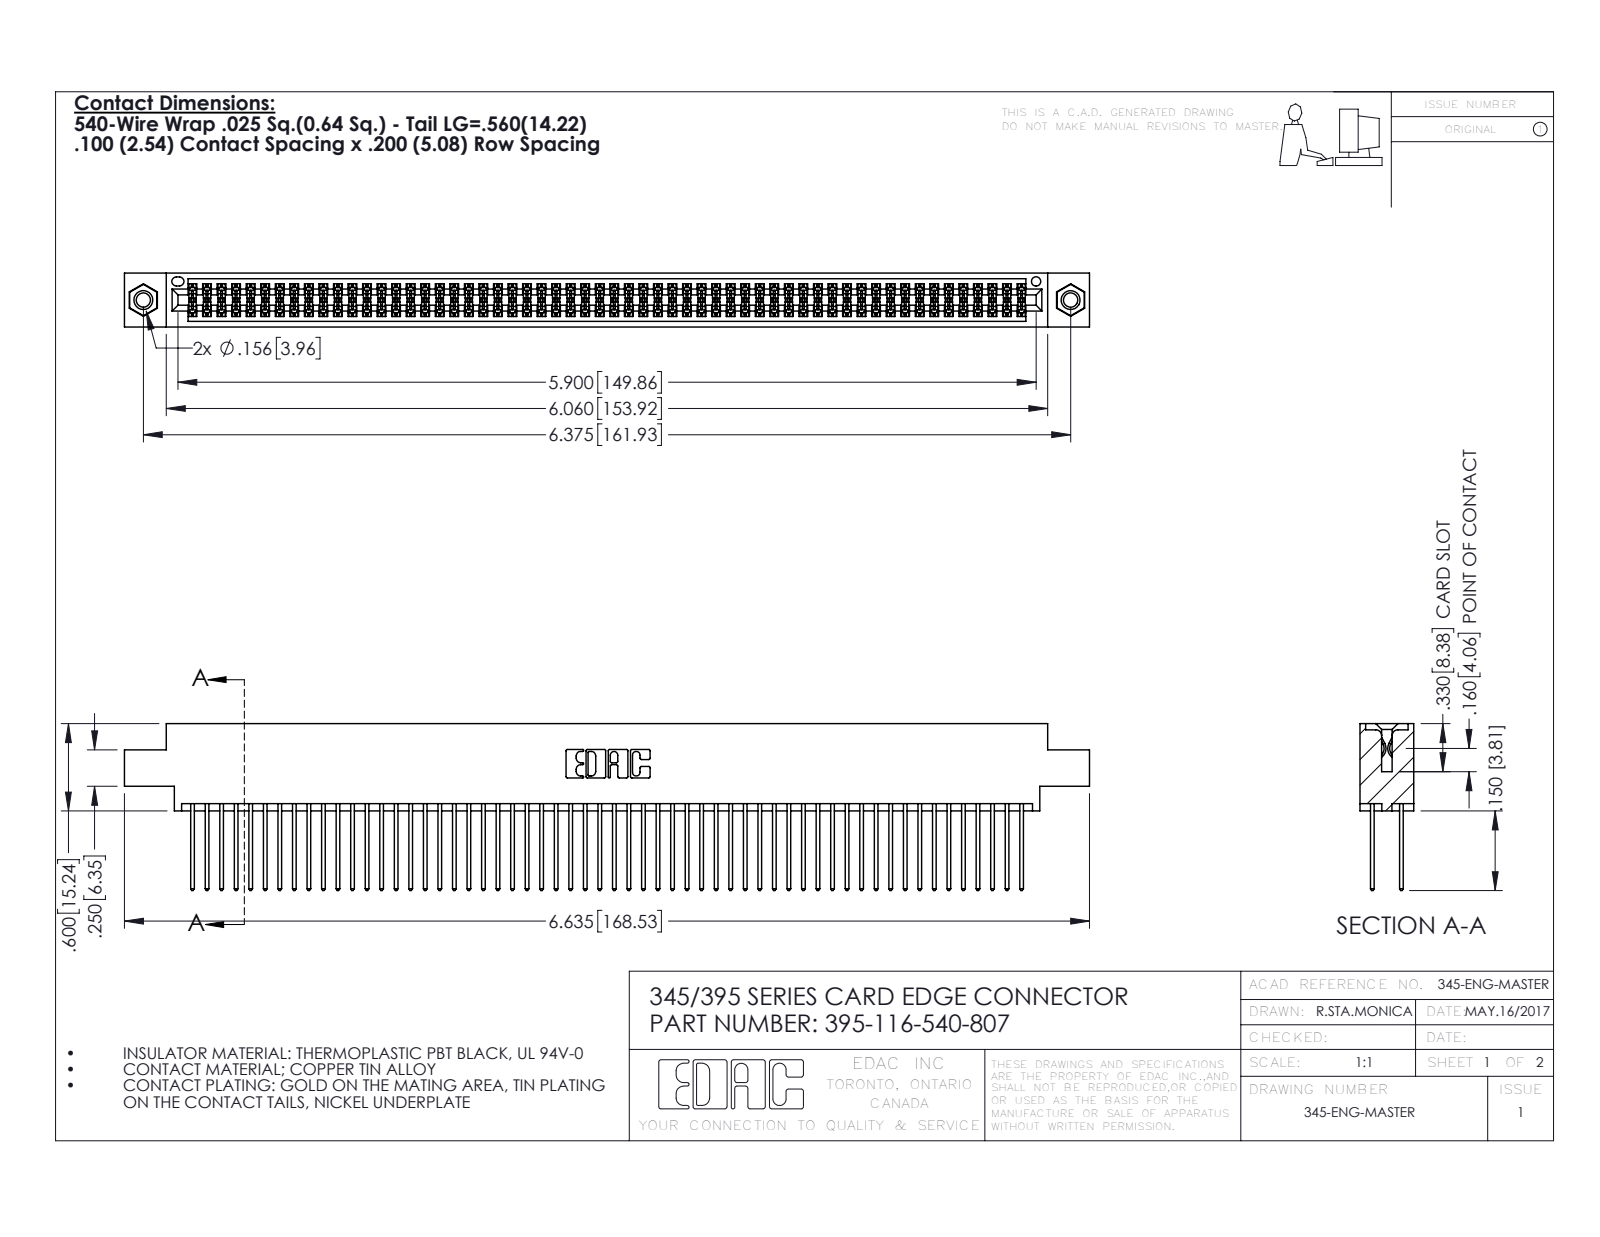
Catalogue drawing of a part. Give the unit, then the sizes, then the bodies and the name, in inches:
Units: inches
Overall size (bounding box): 6.635 × 1.147 × 0.37
Round holes (diameter × count): ⌀0.098 ×2, ⌀0.125 ×2, ⌀0.156 ×2, ⌀0.064 ×1
Round bosses / shafts (diameter × count): ⌀0.155 ×2
Partial cylindrical surfaces — rounded edges, fillets, slot ends (radius × count): R0.006 ×174, R0.01 ×116, R0.01 ×22, R0.007 ×6, R0.031 ×6, R0.026 ×3, R0.014 ×2, R0.019 ×2
Main face-to-face distances: 0.072, 0.298, 0.2, 0.098, 0.272, 0.025, 0.37, 0.225, 0.175, 0.149
Hole centre spacings: 0.27, 6.139, 6.375
Volume: 1.027 in³ · Surface area: 42.47 in²
Bodies: 119 solids, 5990 faces (3944 planar, 2030 cylindrical, 16 other)
Part name (STEP PRODUCT): 345-250-001_345-250-005-103; 395-116-540-807; 345 Part_0.170 Offset - 0.156 Dia-TI; 345-292-001_345-293-140
STEP written by: SolidWorks 2016 (CONFIG_CONTROL_DESIGN)
